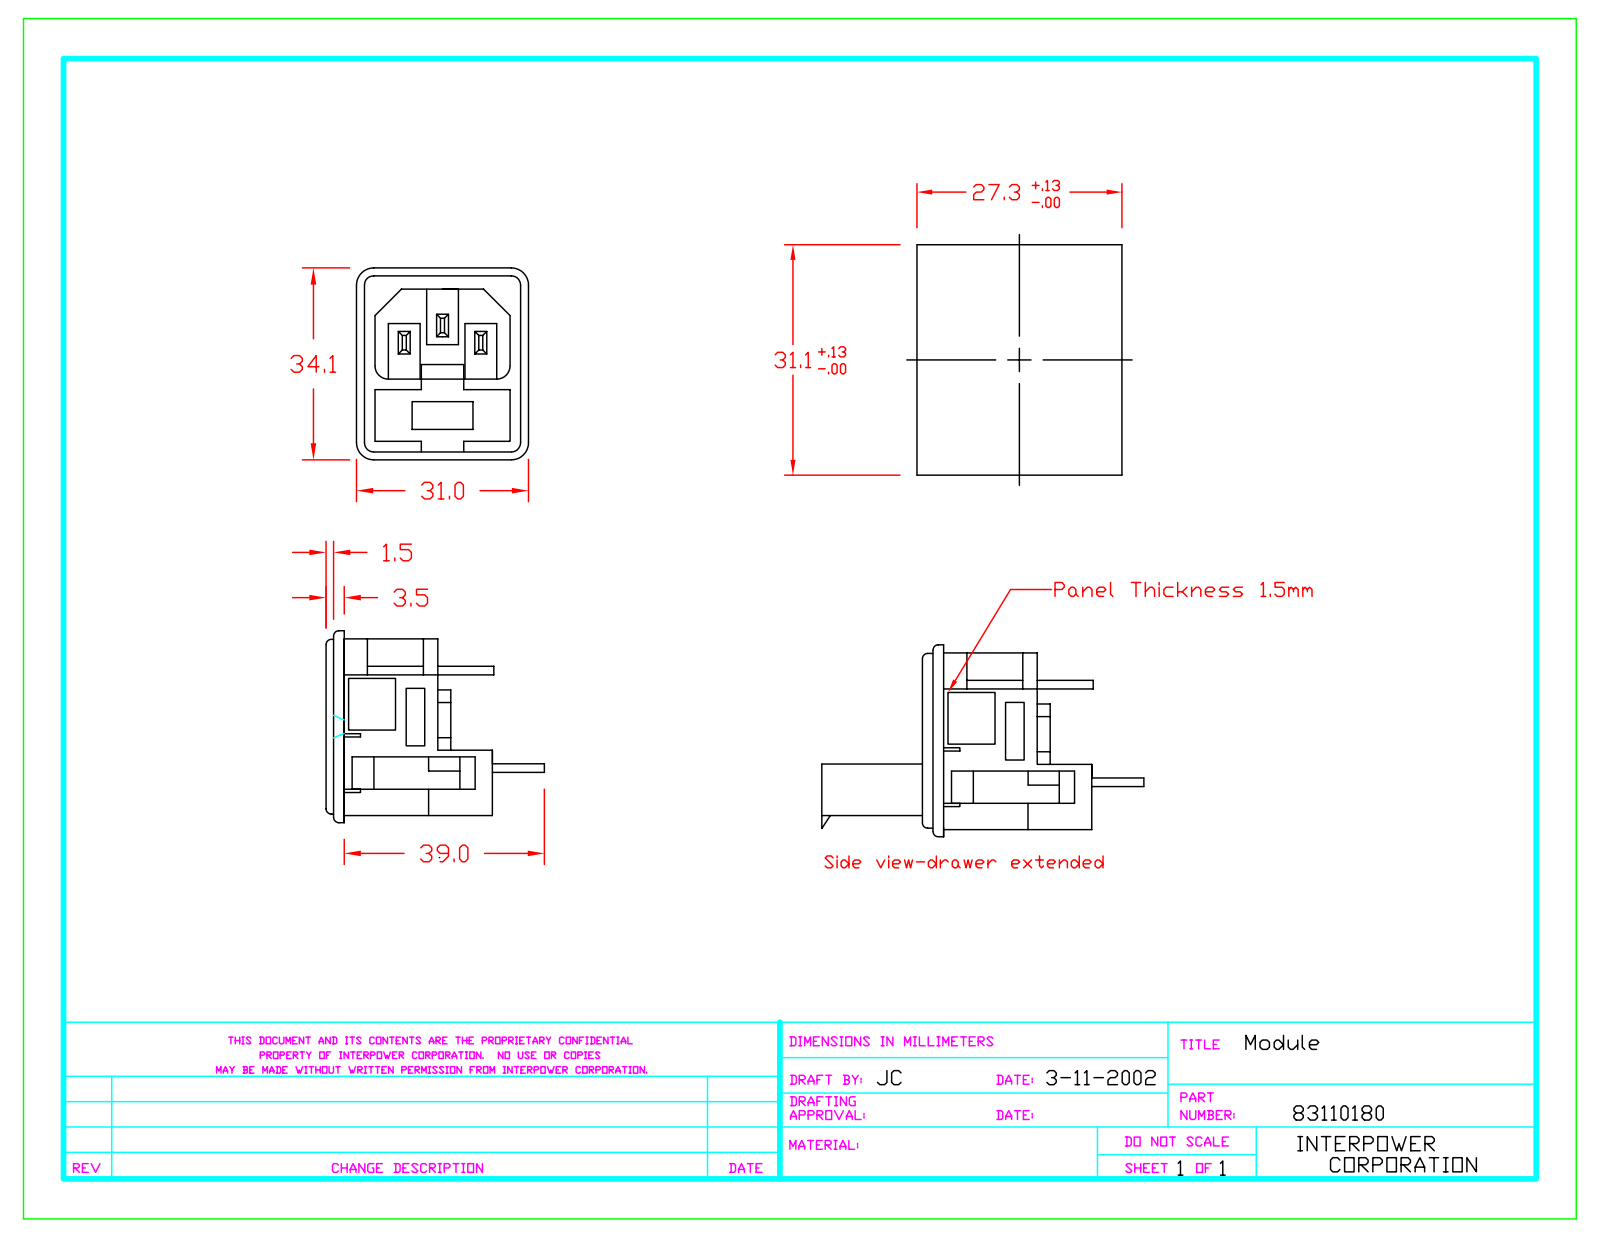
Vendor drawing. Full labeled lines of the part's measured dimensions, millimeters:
Part name (STEP PRODUCT): 83110180
STEP written by: SolidWorks 2007 (CONFIG_CONTROL_DESIGN)
Units: millimetres
Bodies: 1 solid, 279 faces (215 planar, 48 cylindrical, 16 other)
Overall size (bounding box): 42.5 × 34.1 × 30.9
Volume: 12 369 mm³ · Surface area: 11 013 mm²
Round holes (diameter × count): ⌀1.63 ×3
Partial cylindrical surfaces — rounded edges, fillets, slot ends (radius × count): R0.5 ×14, R1.72 ×12, R1.73 ×4, R1.78 ×4, R1.52 ×2
Main face-to-face distances: 1.69, 26.25, 9.51, 1.55, 1.5, 9.07, 21, 13.08, 1.7, 26.24
Hole centre spacings: 13.48, 14.24
